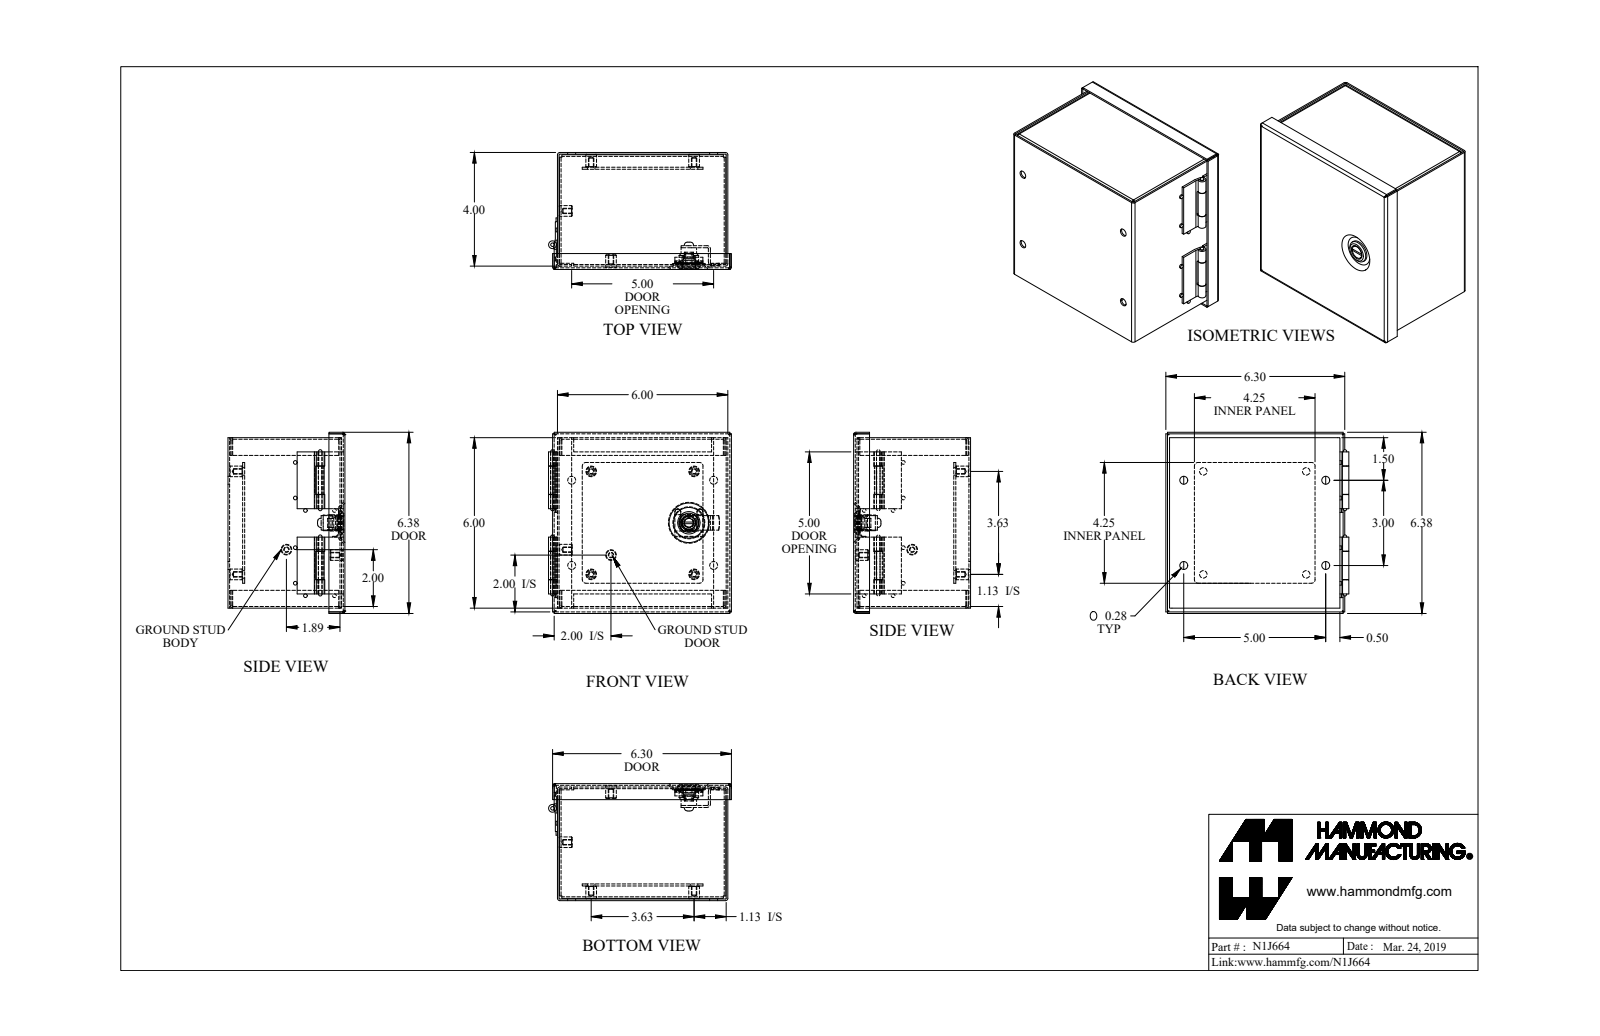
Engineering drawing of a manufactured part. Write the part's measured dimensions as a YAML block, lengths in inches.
part_name: "N1J664"
step_written_by: "SolidWorks 2018 (AUTOMOTIVE_DESIGN)"
units: inches
bodies: {solids: 18, faces: 477, planar: 224, cylindrical: 188, other: 65}
overall_size: [6.443, 6.38, 4.118]
volume: 14.12
surface_area: 484.7
round_holes:
  - {diameter: 0.156, count: 6}
  - {diameter: 0.265, count: 4}
  - {diameter: 0.28, count: 4}
  - {diameter: 0.125, count: 1}
  - {diameter: 0.319, count: 1}
  - {diameter: 0.476, count: 1}
round_bosses_or_shafts:
  - {diameter: 0.131, count: 8}
  - {diameter: 0.375, count: 5}
  - {diameter: 0.787, count: 1}
  - {diameter: 0.547, count: 1}
  - {diameter: 0.472, count: 1}
  - {diameter: 0.469, count: 1}
  - {diameter: 0.375, count: 1}
  - {diameter: 0.366, count: 1}
partial_cylinders:
  - {radius: 0.029, count: 16}
  - {radius: 0.086, count: 16}
  - {radius: 0.012, count: 4}
  - {radius: 0.1, count: 4}
  - {radius: 0.125, count: 4}
  - {radius: 0.036, count: 2}
  - {radius: 0.079, count: 2}
  - {radius: 0.25, count: 2}
face_to_face_distances: [0.057, 5.943, 4.061, 6, 5.886, 4.004, 4.118, 0.072, 0.517, 0.46]
hole_center_spacings: [0.755, 3.383, 3.625, 4.324, 5.438, 3, 5, 5.127]
